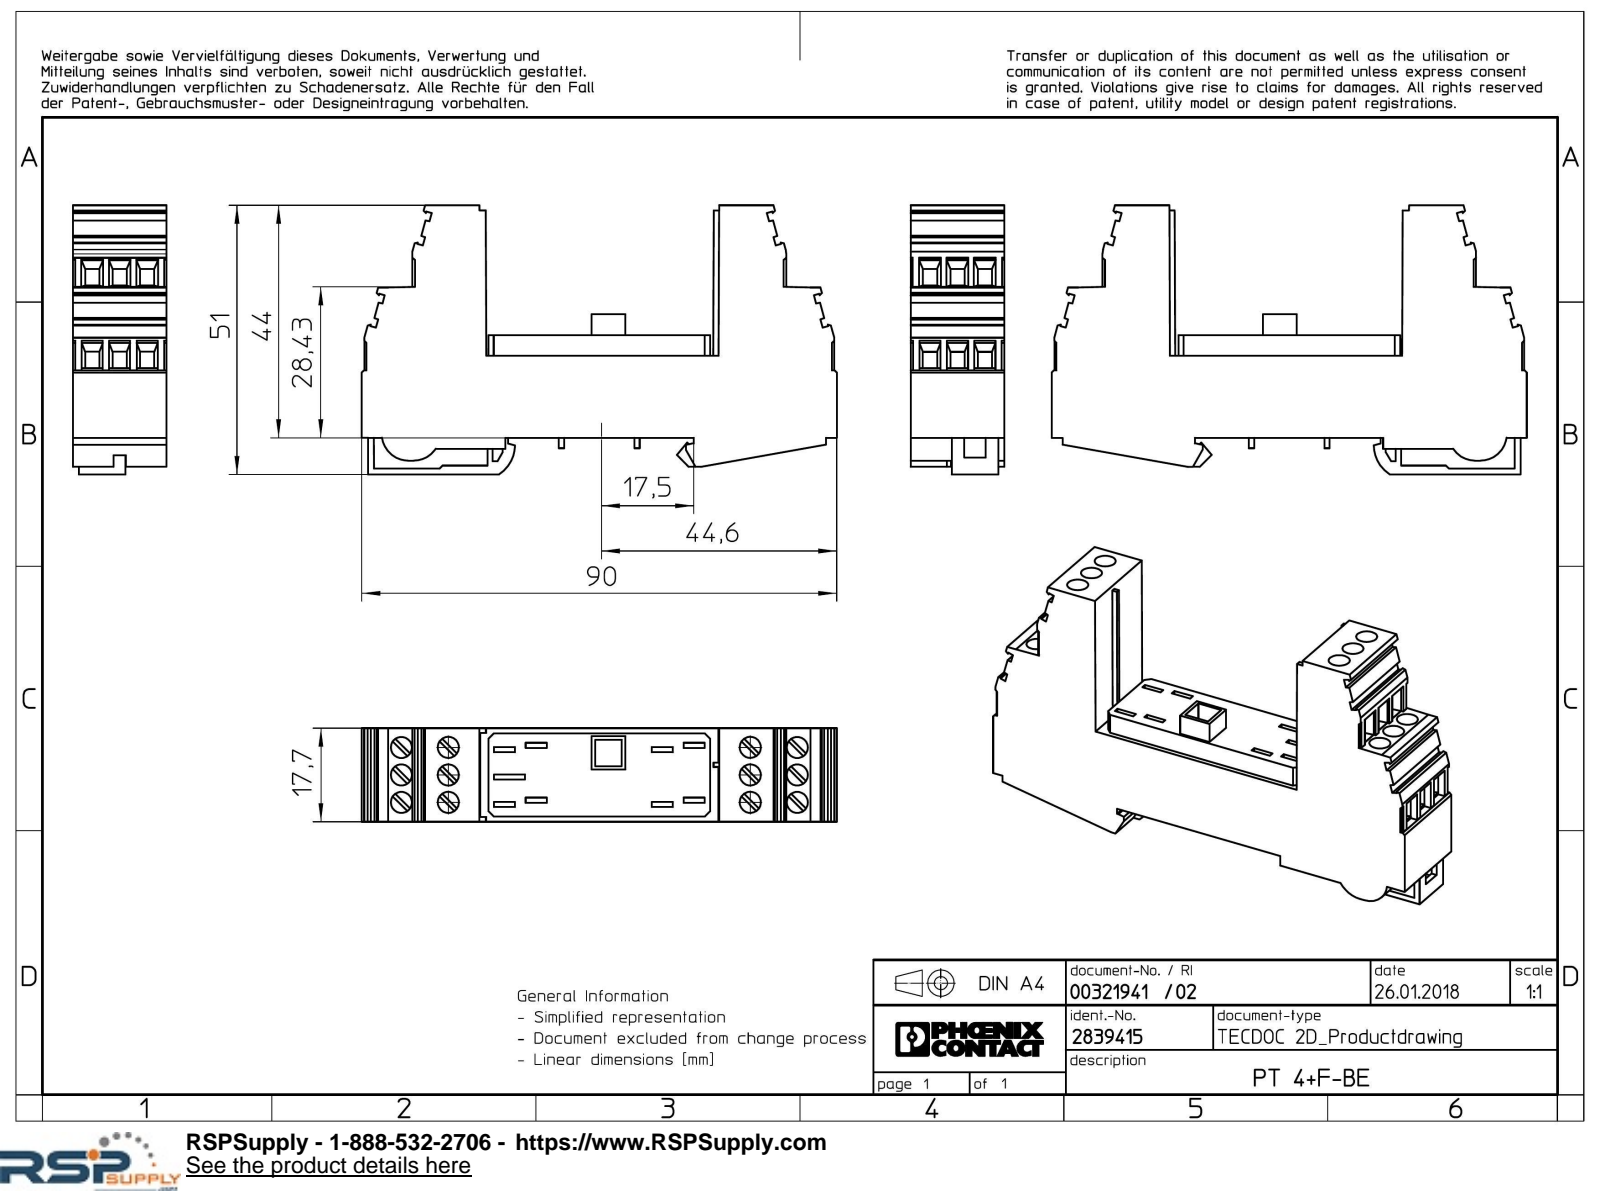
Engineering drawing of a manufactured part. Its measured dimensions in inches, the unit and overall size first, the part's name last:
Units: inches
Overall size (bounding box): 3.543 × 2.006 × 0.697
Round holes (diameter × count): ⌀0.157 ×6
Partial cylindrical surfaces — rounded edges, fillets, slot ends (radius × count): R0.197 ×2, R0.118 ×1, R0.256 ×1
Main face-to-face distances: 0.697, 0.764, 0.205, 0.106, 0.039, 0.176, 0.618, 0.657, 0.846, 1.732
Hole centre spacings: 0.205, 2.261, 2.252, 0.409, 2.289
Volume: 2.682 in³ · Surface area: 23.86 in²
Bodies: 1 solid, 505 faces (477 planar, 16 cylindrical, 12 other)
Part name (STEP PRODUCT): PT...BE-select
STEP written by: Creo Elements/Direct Modeling 20.1A 29-Sep-2018 (C) Parametric Technology GmbH (AUTOMOTIVE_DESIGN)
